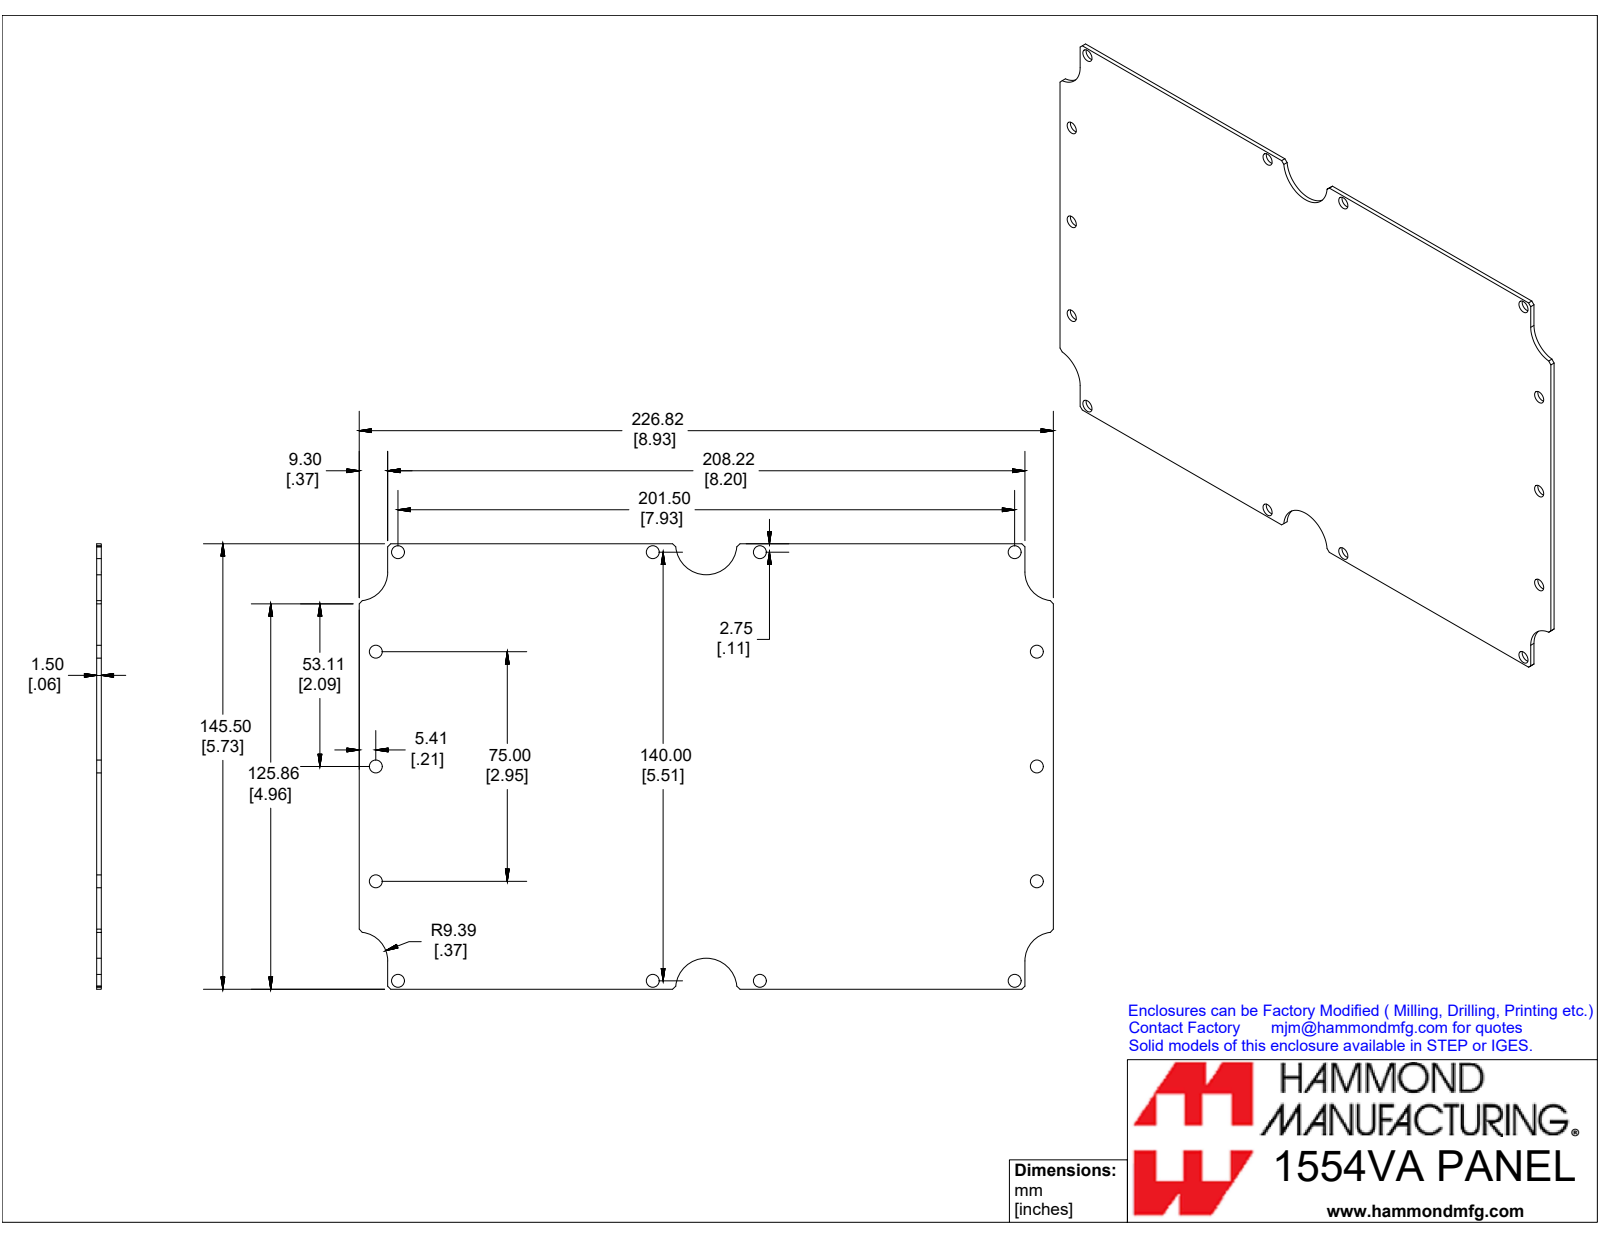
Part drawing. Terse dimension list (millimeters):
name: 1554VAPL
written by: SolidWorks 2019 (CONFIG_CONTROL_DESIGN)
unit: mm
bodies: 1 solid, 44 faces (24 planar, 20 cylindrical, 0 other)
size: 226.8 × 145.5 × 1.5
volume: 47 800 mm³; area: 65 100 mm²
holes: 14× ⌀4.2
rounds: 4× R9.4, 2× R10
face distances: 1.5, 145.5, 226.8, 9.3, 217.5, 208.2, 238.1, 89.5, 248.7
hole spacings: 33.3, 37.5, 70.4, 83.3, 96.2, 107.7, 114.4, 118.3
